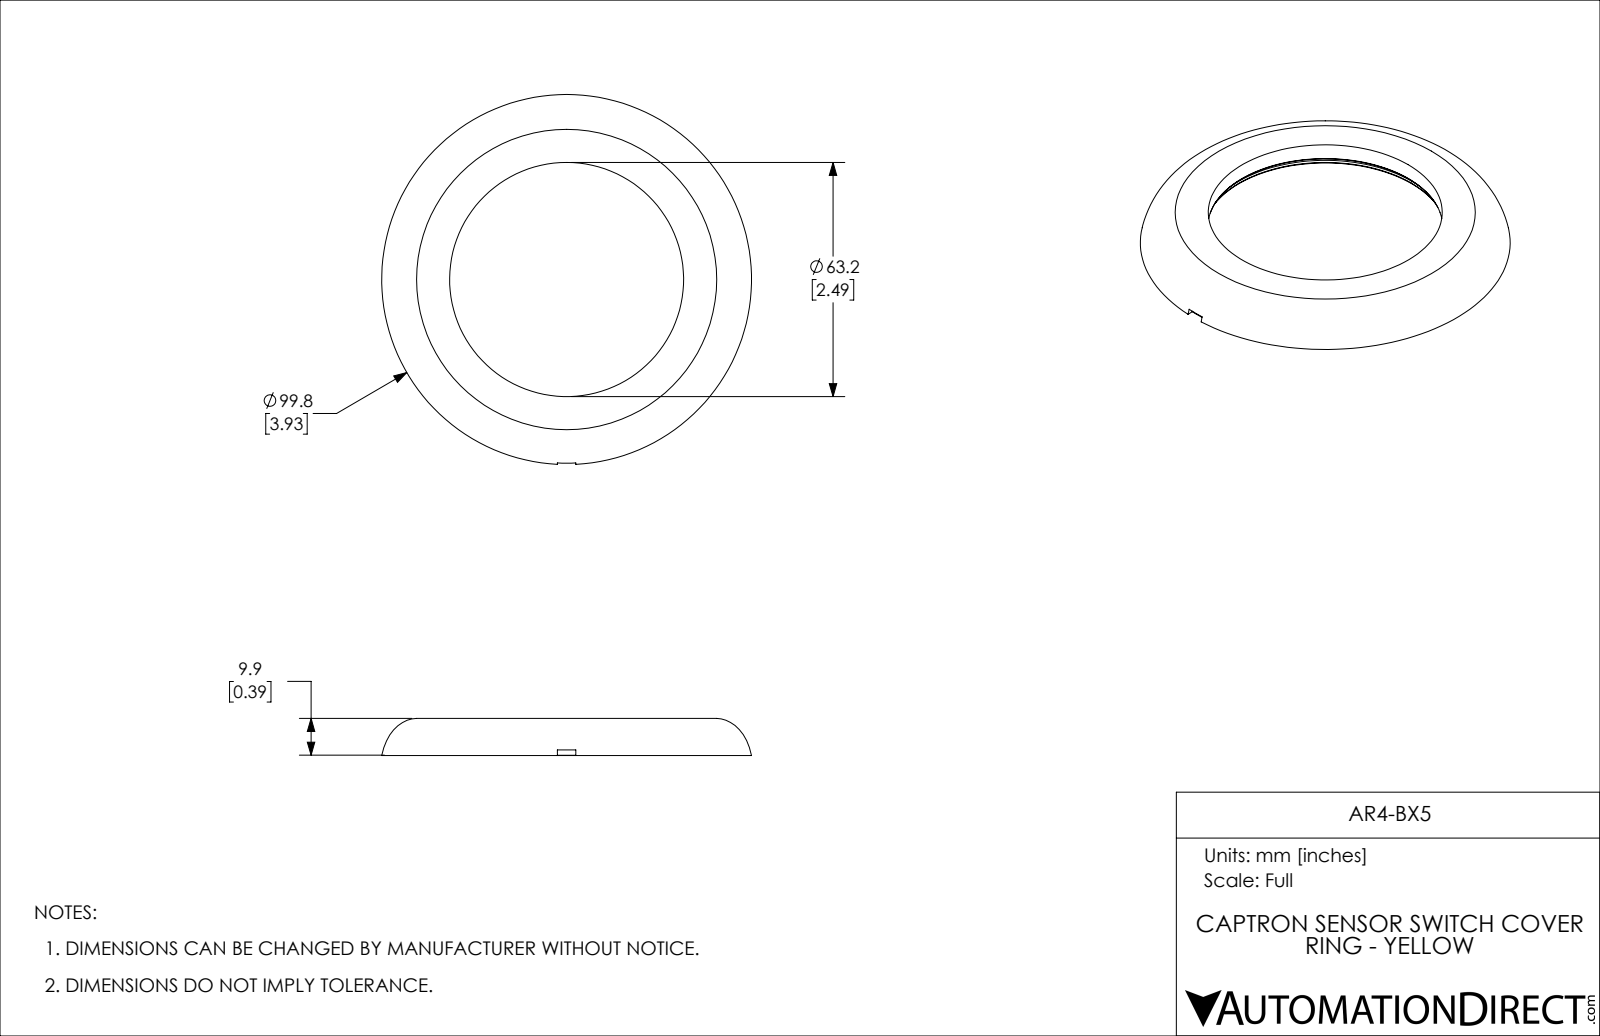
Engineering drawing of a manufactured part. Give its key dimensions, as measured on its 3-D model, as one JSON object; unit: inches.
{"part_name": "AR4-BX5", "step_written_by": "SolidWorks 2019 (CONFIG_CONTROL_DESIGN)", "units": "inches", "bodies": {"solids": 1, "faces": 49, "planar": 7, "cylindrical": 4, "other": 38}, "overall_size": [3.929, 3.927, 0.394], "volume_in3": 0.743, "surface_area_in2": 22.88, "round_holes": [[2.583, 1], [3.714, 1]], "face_to_face_distances": [0.079, 0.197, 0.276, 0.087, 0.11, 0.189, 0.059, 0.146, 0.256, 0.335]}
